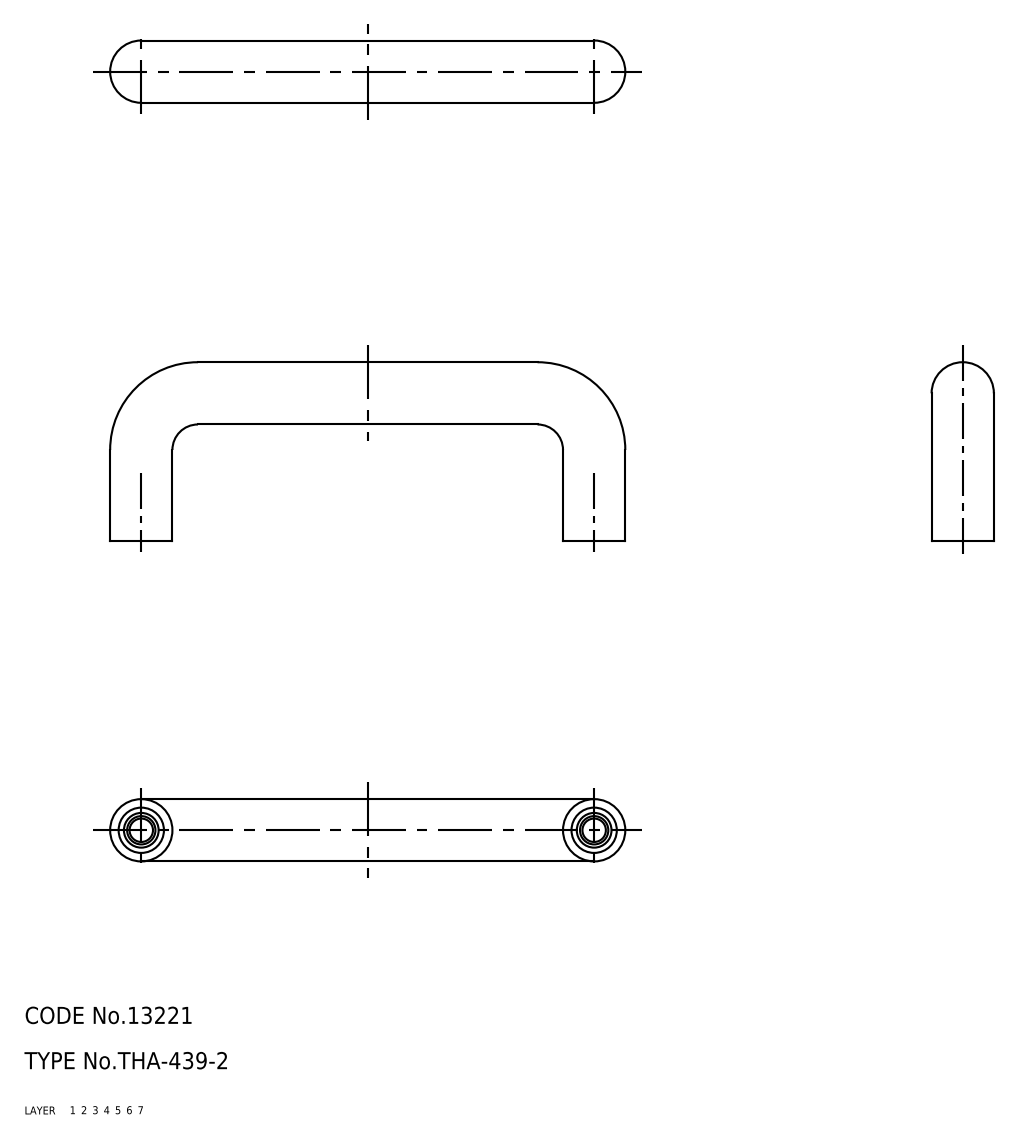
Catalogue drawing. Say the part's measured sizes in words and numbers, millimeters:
The part is named "pull; coat; THA_439_2_1590_36". Its 3-D file was written by "CADfix (AUTOMOTIVE_DESIGN)". It is 2 solids with 40 faces: 0 planar, 0 cylindrical and 40 other. Overall it measures 91 by 31.5 by 11 millimeters. Its volume is 11 271 cubic millimeters and its surface area 11 039 square millimeters.
